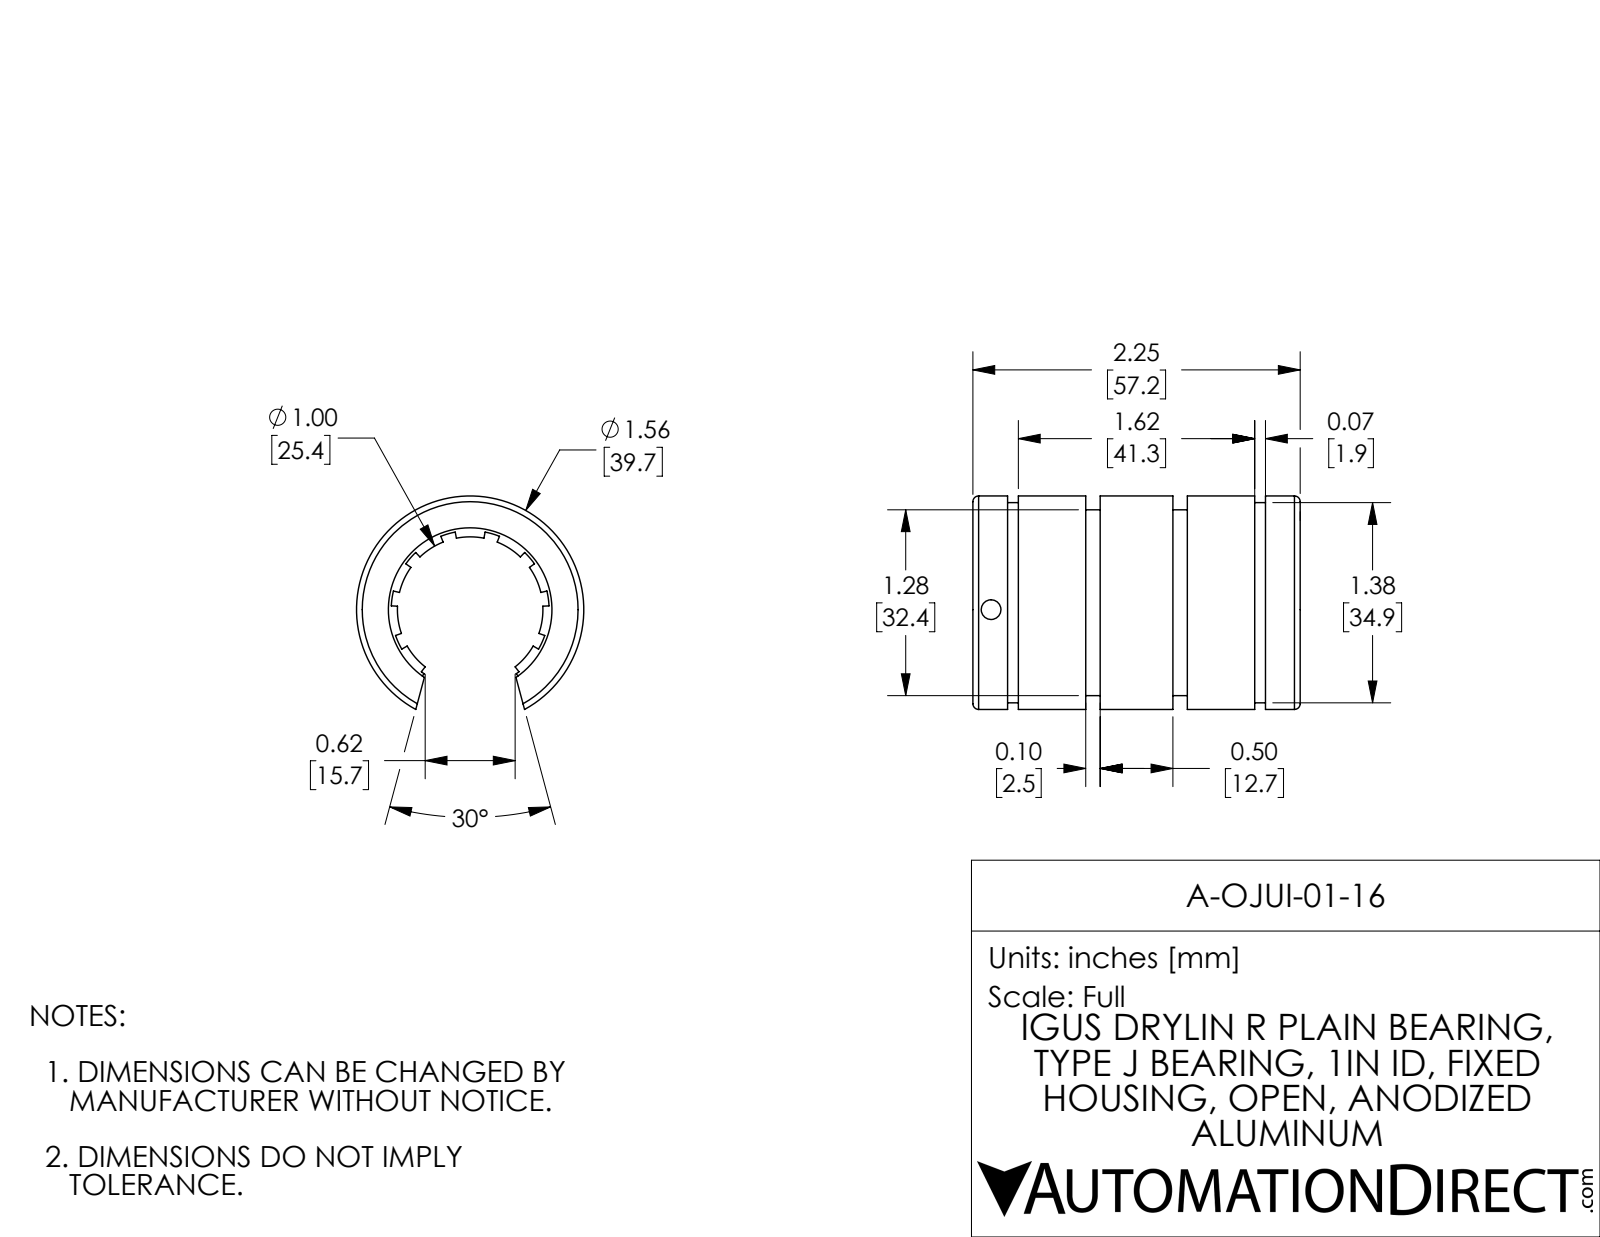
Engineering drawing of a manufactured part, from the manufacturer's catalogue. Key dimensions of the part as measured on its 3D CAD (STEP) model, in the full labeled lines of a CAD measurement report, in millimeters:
Part name (STEP PRODUCT): A-OJUI-01-16
STEP written by: SolidWorks 2017 (AUTOMOTIVE_DESIGN)
Units: millimetres
Bodies: 2 solids, 124 faces (73 planar, 45 cylindrical, 6 other)
Overall size (bounding box): 57.2 × 39.7 × 37.3
Volume: 31 100 mm³ · Surface area: 22 410 mm²
Round holes (diameter × count): ⌀3.5 ×1, ⌀28.6 ×1, ⌀30.6 ×1
Round bosses / shafts (diameter × count): ⌀39.7 ×1, ⌀37.4 ×1, ⌀34.8 ×1, ⌀28.6 ×1, ⌀3.8 ×1
Partial cylindrical surfaces — rounded edges, fillets, slot ends (radius × count): R12.7 ×1, R13.8 ×1, R15.1 ×1
Main face-to-face distances: 19.7, 22.2, 34.9, 37.4, 15.2, 2.5, 57.2, 17.7, 12.7, 6.1
